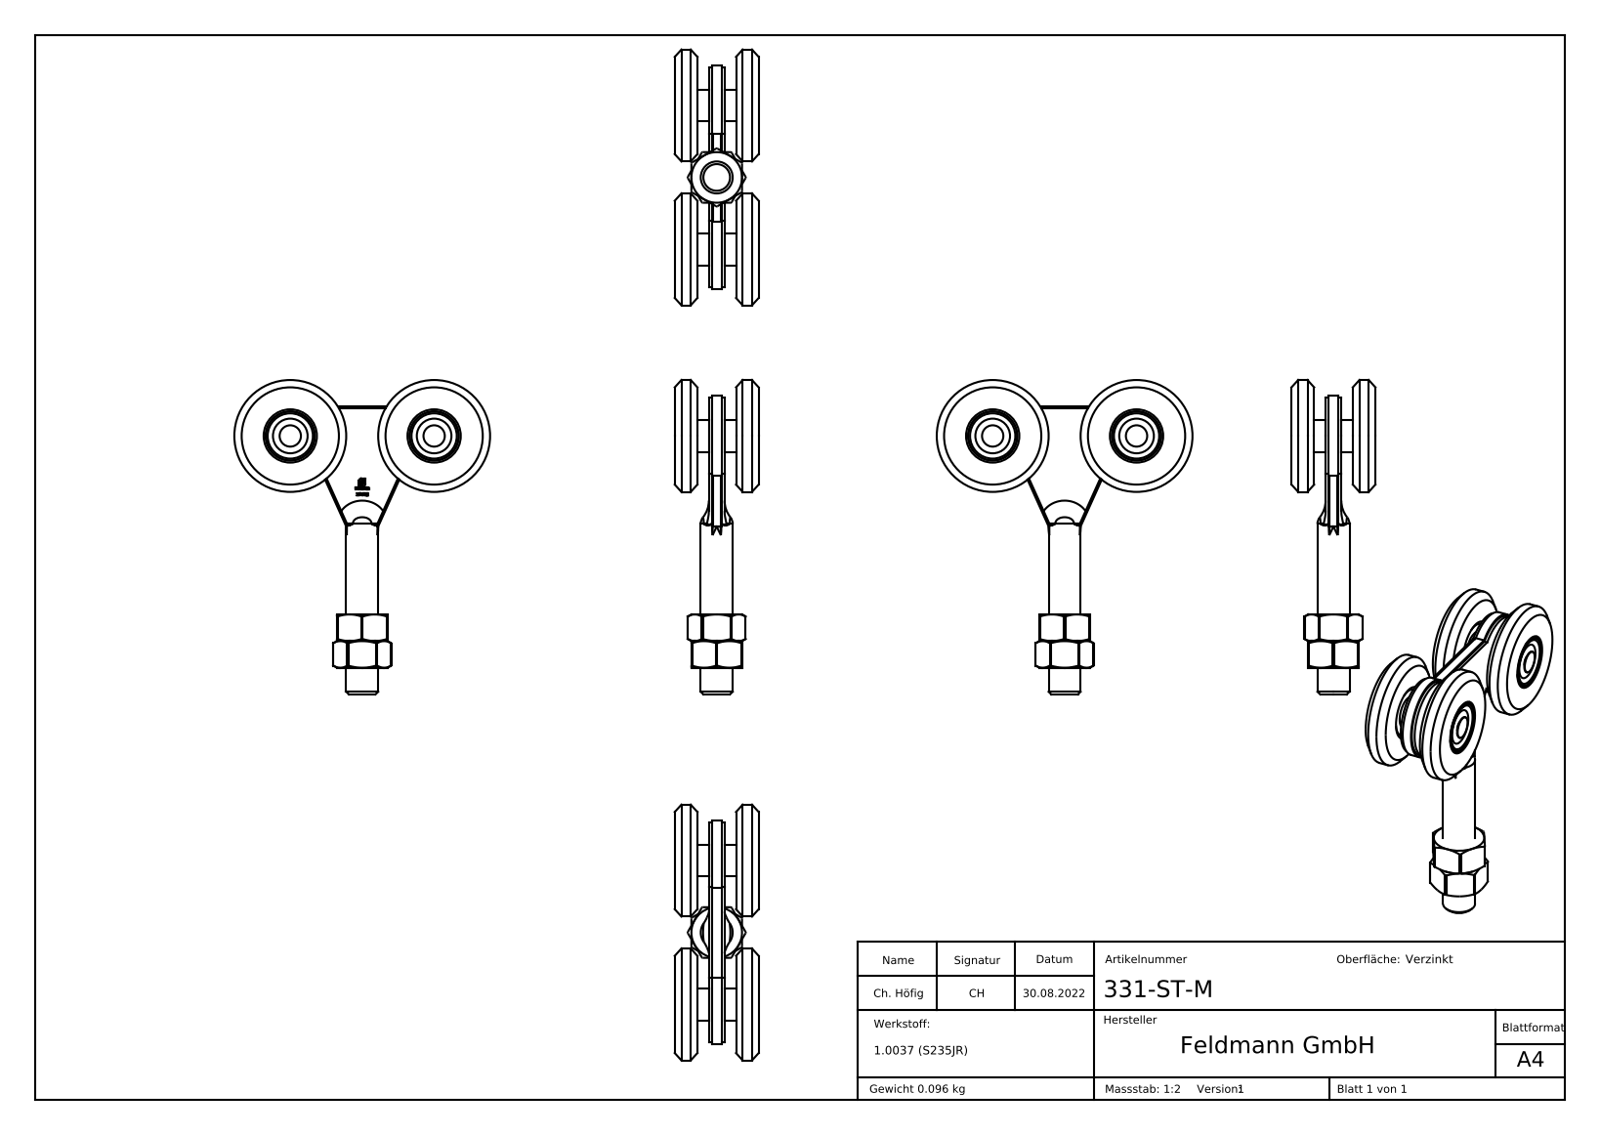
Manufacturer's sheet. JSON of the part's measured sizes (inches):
{"part_name": "331-ST-M; 331-X-X Teil1_331-ST-M Teil1; DIN 934 M4-M20_DIN 934 M12", "step_written_by": "SolidWorks 2018 (CONFIG_CONTROL_DESIGN)", "units": "inches", "bodies": {"solids": 17, "faces": 520, "planar": 233, "cylindrical": 81, "other": 206}, "overall_size": [4.646, 3.78, 1.24], "volume_in3": 4.25, "surface_area_in2": 48.41, "round_holes": [[0.197, 2], [0.701, 2], [0.787, 2], [0.402, 1]], "round_bosses_or_shafts": [[0.472, 3], [1.654, 2], [0.728, 2], [0.315, 2], [0.189, 2]], "partial_cylinders_radius": [[0.02, 12], [0.01, 6], [0.394, 4], [0.563, 2], [0.591, 2]], "face_to_face_distances": [0.906, 0.504, 0.736, 0.232, 0.335, 0.169, 0.402, 0.051, 0.283, 0.453], "hole_center_spacings": [2.126]}
